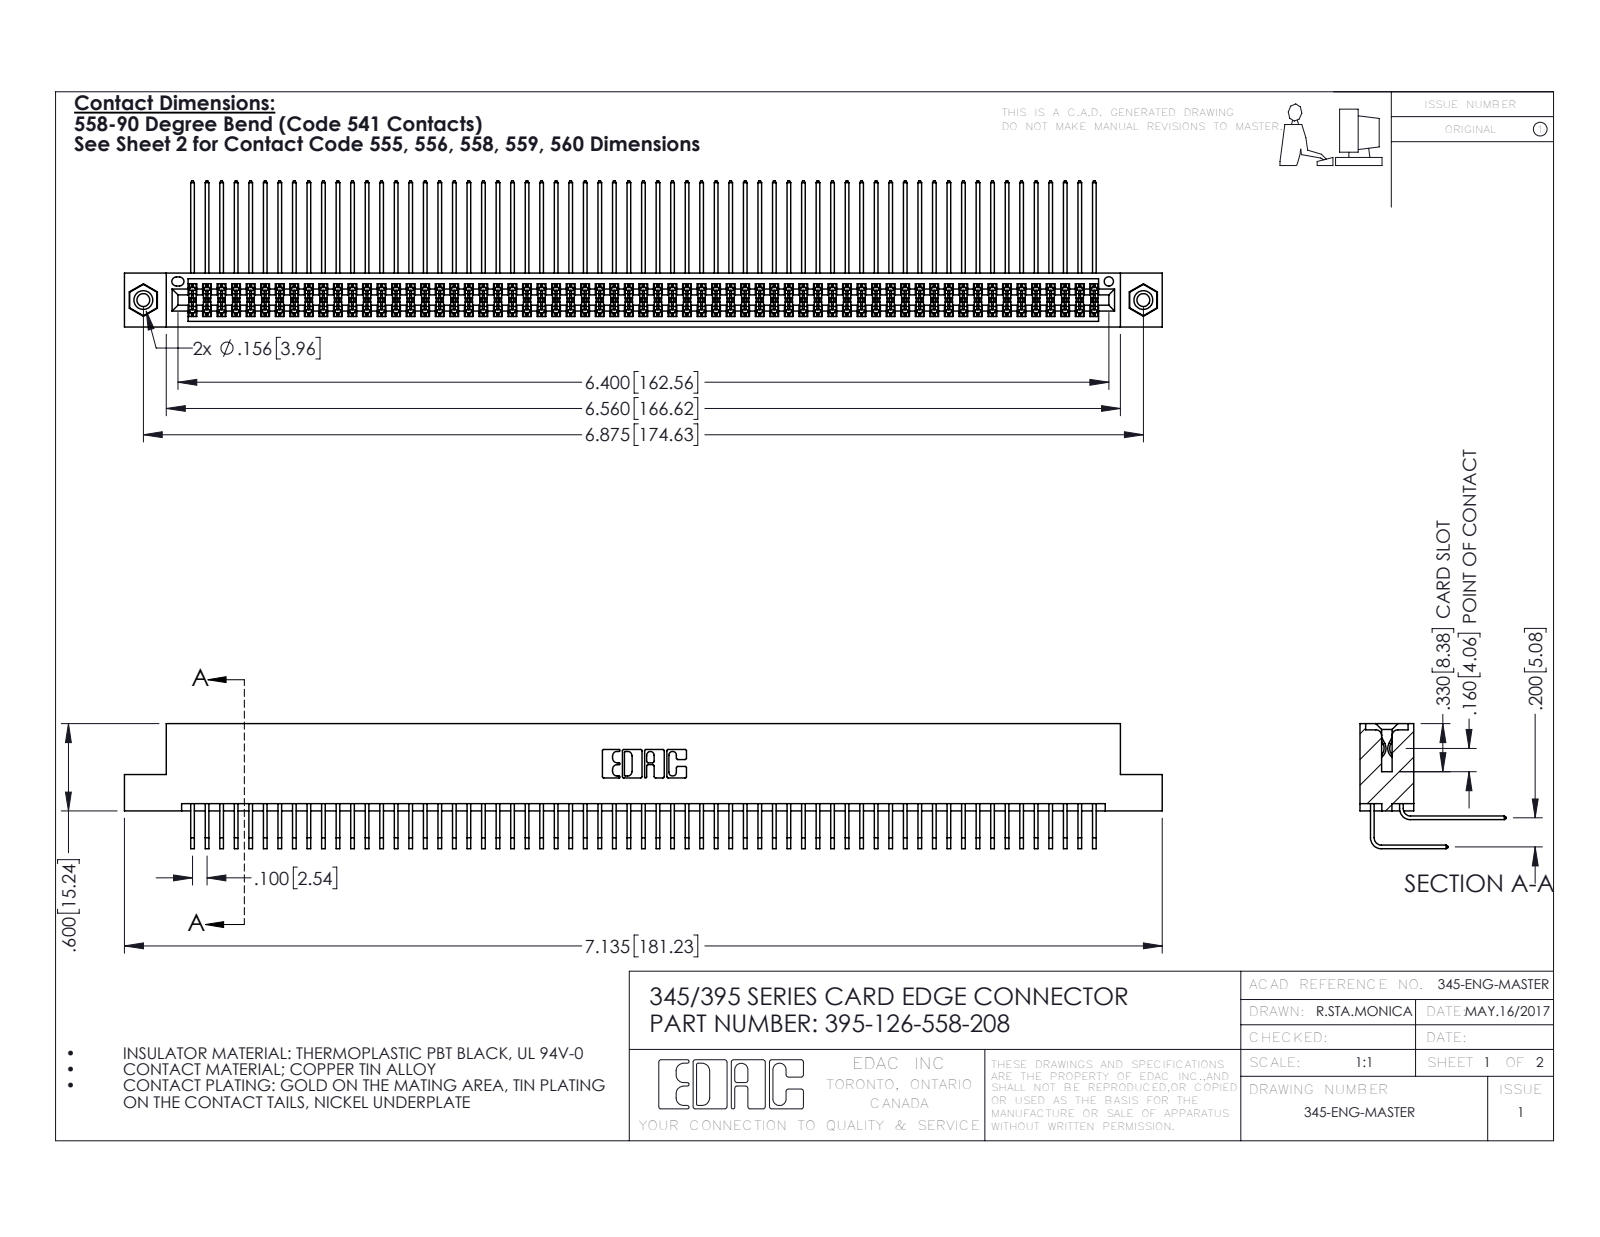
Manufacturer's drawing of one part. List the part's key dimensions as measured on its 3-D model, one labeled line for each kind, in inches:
Part name (STEP PRODUCT): 345-250-001_345-250-003-102; 345-292-001_558 Tail - 2; 345-292-001_558 559 Tail - 1; 395-126-558-208 (+1 more)
STEP written by: SolidWorks 2016 (CONFIG_CONTROL_DESIGN)
Units: inches
Bodies: 129 solids, 6738 faces (4522 planar, 2200 cylindrical, 16 other)
Overall size (bounding box): 7.135 × 1.005 × 0.859
Volume: 1.13 in³ · Surface area: 48.38 in²
Round holes (diameter × count): ⌀0.089 ×2, ⌀0.125 ×2, ⌀0.156 ×2, ⌀0.064 ×1
Round bosses / shafts (diameter × count): ⌀0.155 ×2
Partial cylindrical surfaces — rounded edges, fillets, slot ends (radius × count): R0.006 ×190, R0.01 ×22, R0.007 ×6, R0.031 ×6, R0.026 ×3, R0.014 ×2, R0.019 ×2, R0.022 ×2
Main face-to-face distances: 0.072, 0.298, 0.2, 0.37, 0.098, 0.272, 0.025, 0.225, 0.025, 0.175
Hole centre spacings: 0.27, 6.639, 6.875
